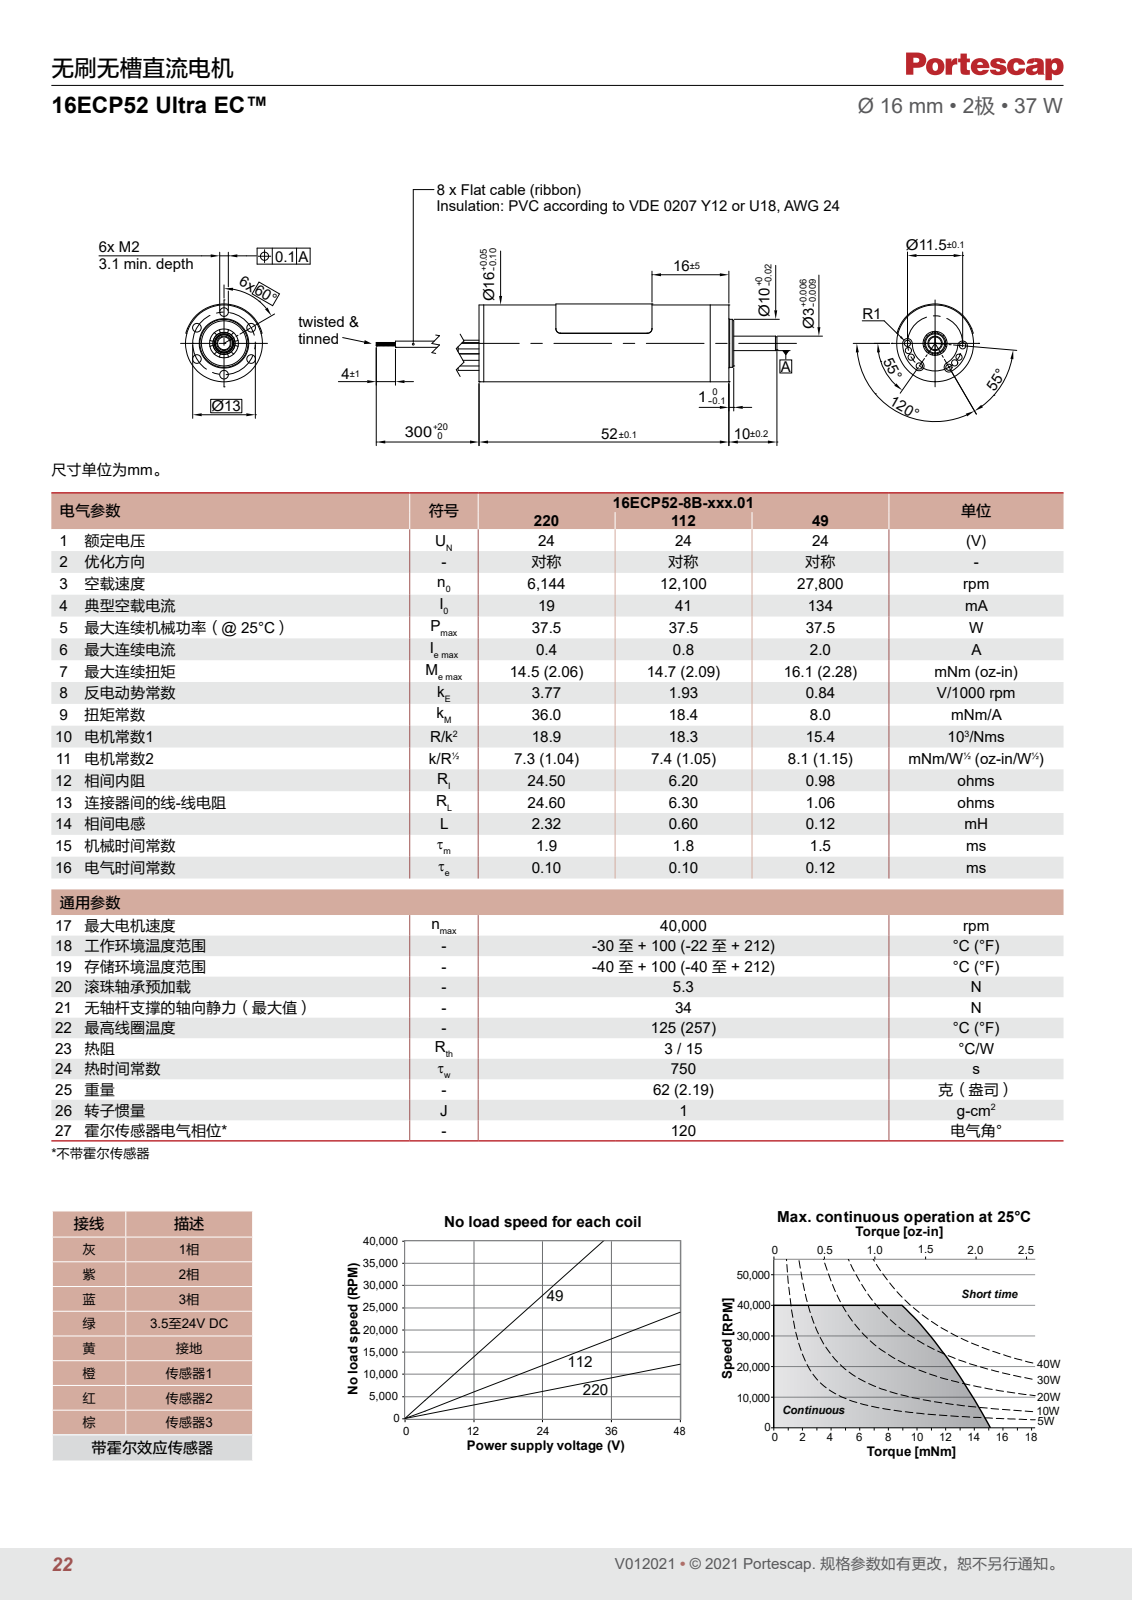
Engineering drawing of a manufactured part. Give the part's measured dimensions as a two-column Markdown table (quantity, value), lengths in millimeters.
| quantity | value |
| --- | --- |
| part name | 16ECP52 |
| STEP written by | PRO/ENGINEER BY PARAMETRIC TECHNOLOGY CORPORATION, 2014310 (CONFIG_CONTROL_DESIGN) |
| units | millimeters |
| bodies | 9 solids, 263 faces (41 planar, 111 cylindrical, 111 other) |
| overall size | 137 × 16.2 × 16 |
| volume | 11 193 mm³ |
| surface area | 6 315 mm² |
| round holes (diameter × count) | 1.6 × 6, 3 × 1, 5 × 1, 5.6 × 1, 6 × 1, 6.4 × 1, 7 × 1, 8 × 1 |
| round bosses / shafts (diameter × count) | 1.3 × 8, 0.7 × 8, 16 × 1, 10 × 1, 4.6 × 1, 4.4 × 1 |
| partial cylindrical surfaces (radius × count) | 1 × 8, 4.75 × 1, 6.75 × 1, 8.2 × 1 |
| main face-to-face distances | 52, 0.5, 52.5, 53, 1, 3, 49, 50, 49.5, 2.5 |
| hole center spacings | 6.5, 11.26, 13 |
